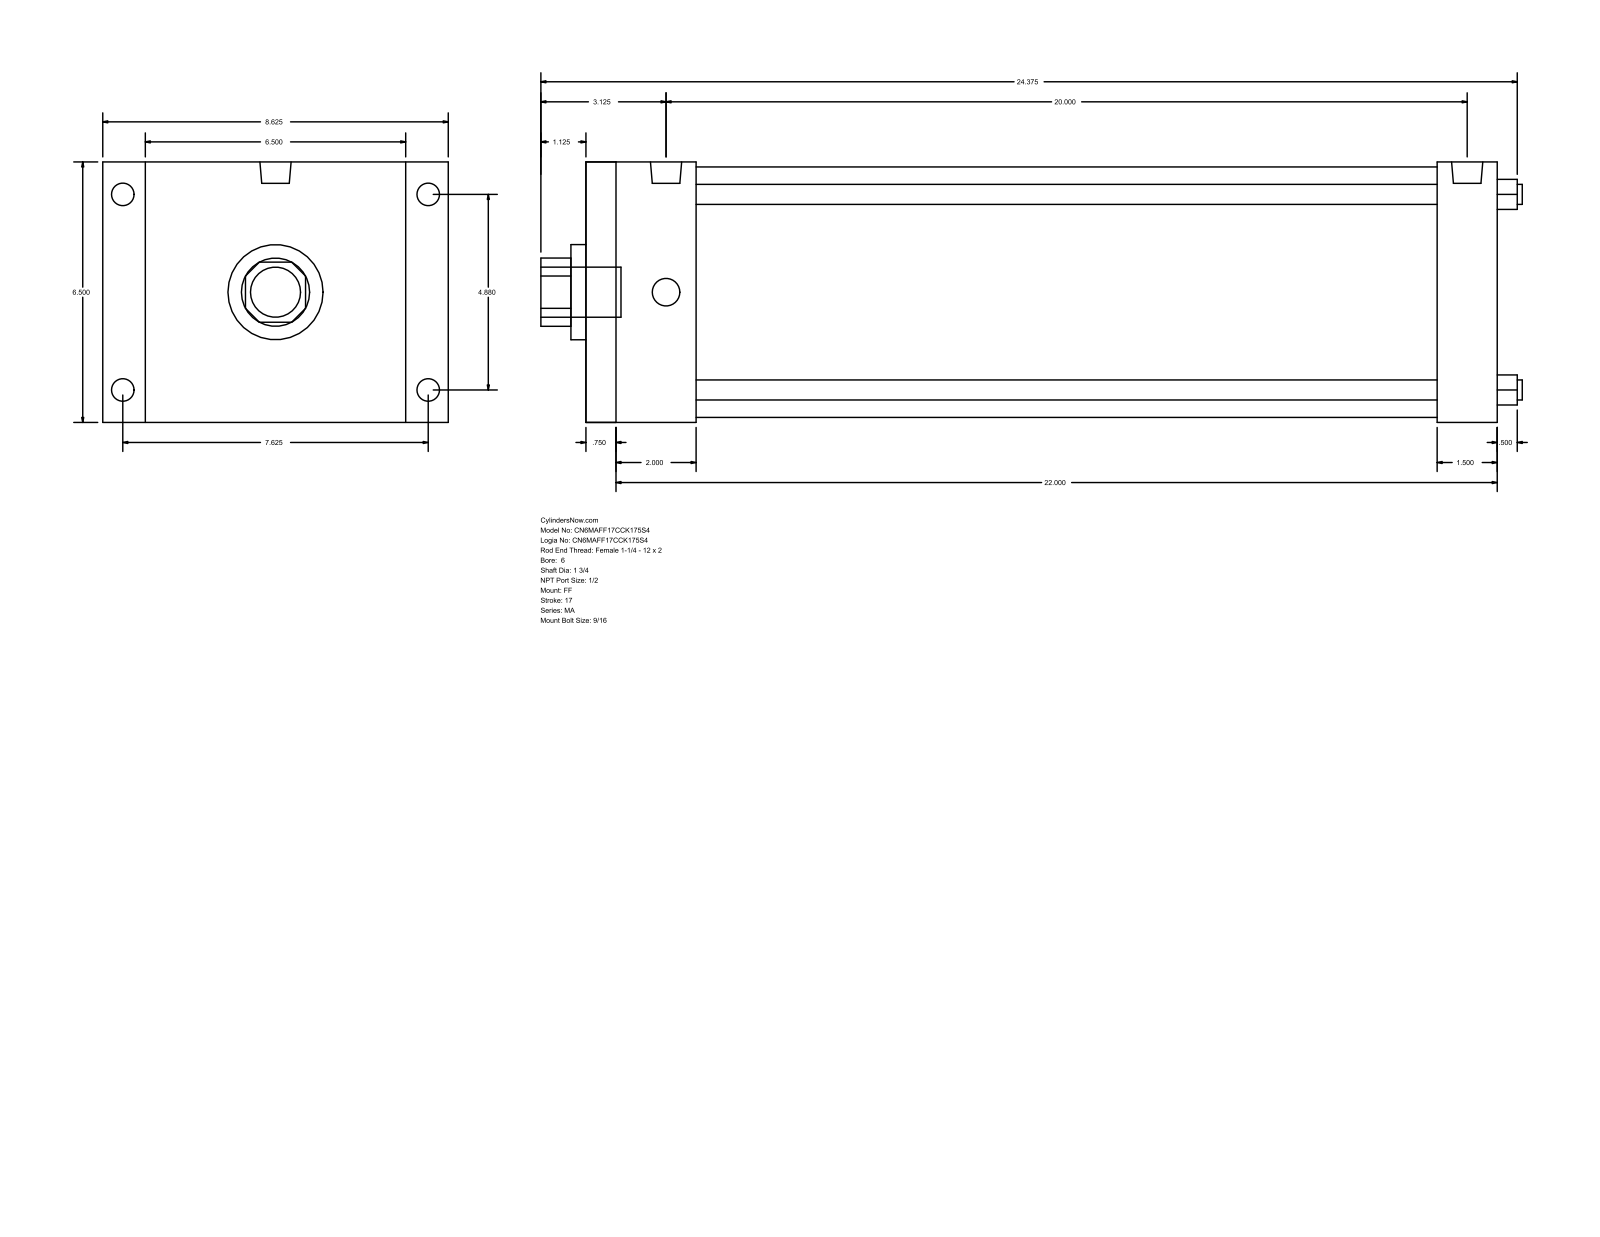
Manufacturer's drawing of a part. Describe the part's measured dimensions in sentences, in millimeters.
The part is named "MA_FF__0600_1.75". Its 3-D file was written by "GSSL Pune (CONFIG_CONTROL_DESIGN)". It is 0 solids with 92 faces: 64 planar, 28 cylindrical and 0 other. Overall it measures 622.3 by 219.07 by 165.1 millimeters. Round holes: 4 of diameter 12.7, 1 of diameter 44.45, 1 of diameter 60.33, 1 of diameter 158.75. Round bosses or shafts: 4 of diameter 17.46, 4 of diameter 14.29, 2 of diameter 19.77, 1 of diameter 31.75. Partial cylindrical surfaces (rounded edges, fillets, slot ends): 1 of radius 21.63. The main face-to-face distances are 165.1, 577.85, 19.05, 558.8, 50.8, 69.85, 508, 539.76, 520.71, 469.91. The hole center spacings are 87.65, 123.96, 175.31.
